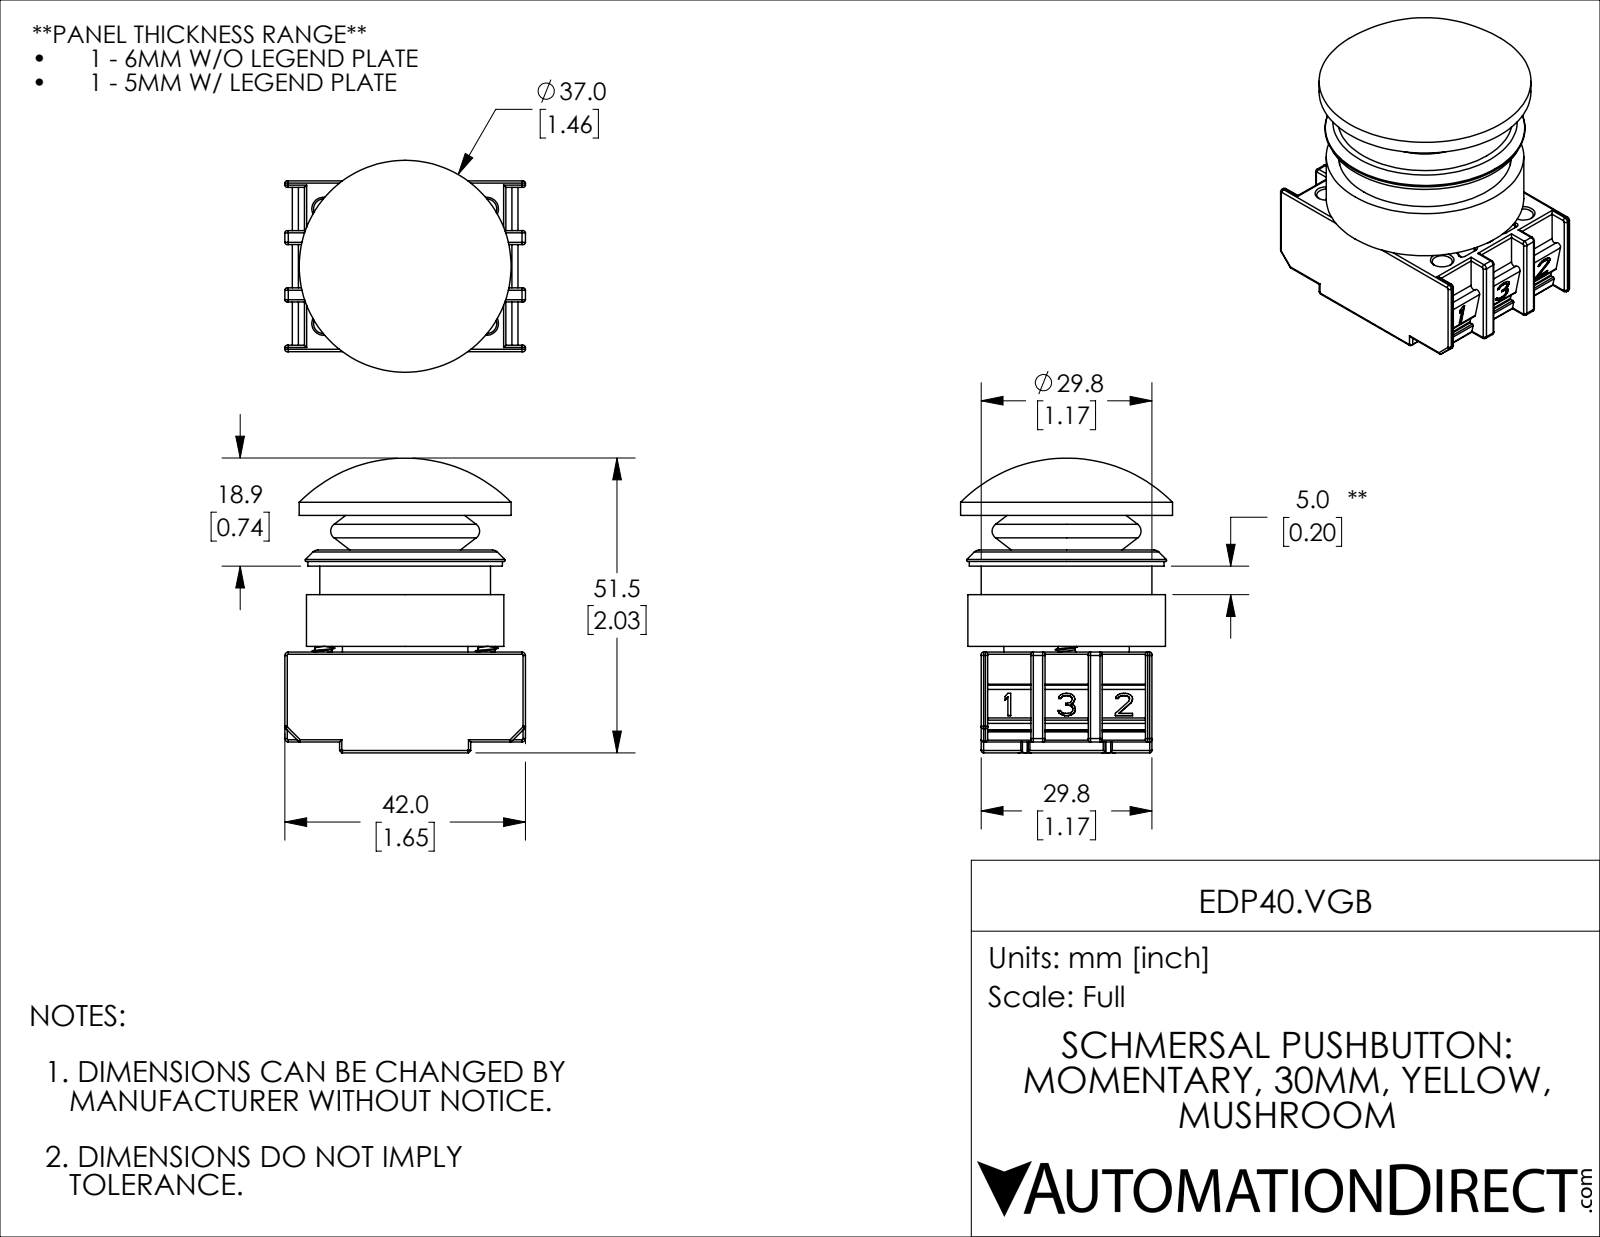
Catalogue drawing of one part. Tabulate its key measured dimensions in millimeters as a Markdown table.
| quantity | value |
| --- | --- |
| part name | EDP40.VGB |
| STEP written by | SolidWorks 2019 (CONFIG_CONTROL_DESIGN) |
| units | millimeters |
| bodies | 5 solids, 1490 faces (538 planar, 503 cylindrical, 449 other) |
| overall size | 51.45 × 42 × 37 |
| volume | 32 755 mm³ |
| surface area | 23 609 mm² |
| round holes (diameter × count) | 3.5 × 6, 5.15 × 6, 8.25 × 1, 12.15 × 1, 18.8 × 1, 19.5 × 1, 24.1 × 1, 24.2 × 1, 26 × 1, 30.2 × 1, 32 × 1 |
| round bosses / shafts (diameter × count) | 4.8 × 2, 2.93 × 2, 37 × 1, 34.5 × 1, 34 × 1, 29.8 × 1, 25.5 × 1, 24 × 1 |
| partial cylindrical surfaces (radius × count) | 0.4 × 112, 0.3 × 48, 0.2 × 28, 0.6 × 8, 0.5 × 6, 0.8 × 6, 0.1 × 2, 0.6 × 2 |
| main face-to-face distances | 18.6, 29.8, 1, 1.9, 16.8, 17.6, 35.4, 17.8, 20.95, 10 |
| hole center spacings | 10, 17.41, 30.2, 28.5, 14.25, 20, 34.82 |
